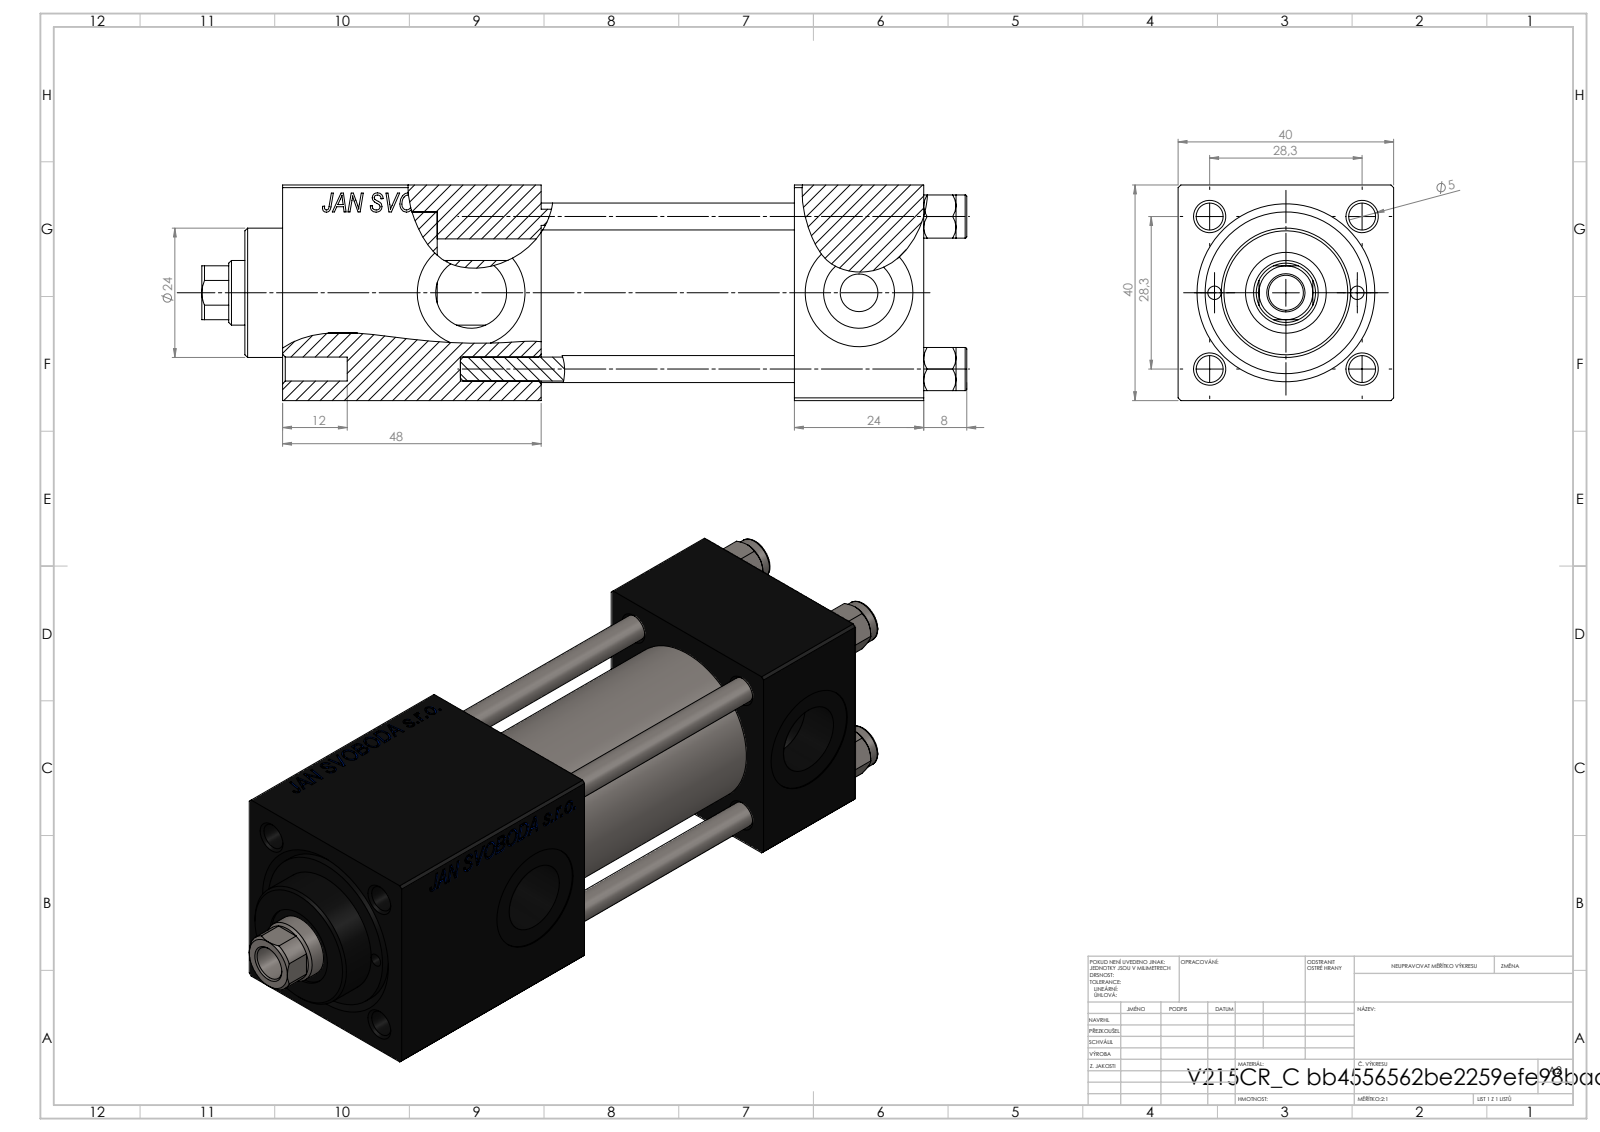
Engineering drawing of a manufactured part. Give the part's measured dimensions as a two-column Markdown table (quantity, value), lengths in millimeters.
| quantity | value |
| --- | --- |
| part name | NUT_M5_C; V215CR_C_TYCINKA; V215CR_VCP_C; V215CR_C_Body (+1 more) |
| STEP written by | SolidWorks 2019 (CONFIG_CONTROL_DESIGN) |
| units | millimeters |
| bodies | 11 solids, 1153 faces (527 planar, 90 cylindrical, 536 other) |
| overall size | 142 × 40 × 40 |
| volume | 142 591 mm³ |
| surface area | 54 456 mm² |
| round holes (diameter × count) | 5 × 4, 20 × 3, 2.5 × 2, 7 × 2, 13.16 × 2, 6.5 × 1, 12 × 1, 15 × 1, 25 × 1, 30 × 1 |
| round bosses / shafts (diameter × count) | 8 × 4, 31 × 1, 24 × 1 |
| partial cylindrical surfaces (radius × count) | 5.5 × 1 |
| main face-to-face distances | 40, 24, 90.3, 66.3, 48, 71, 47, 19.3, 119, 95 |
| hole center spacings | 14.18, 20.01, 28.3, 30.84, 13.25, 40.02, 26.5, 72 |
